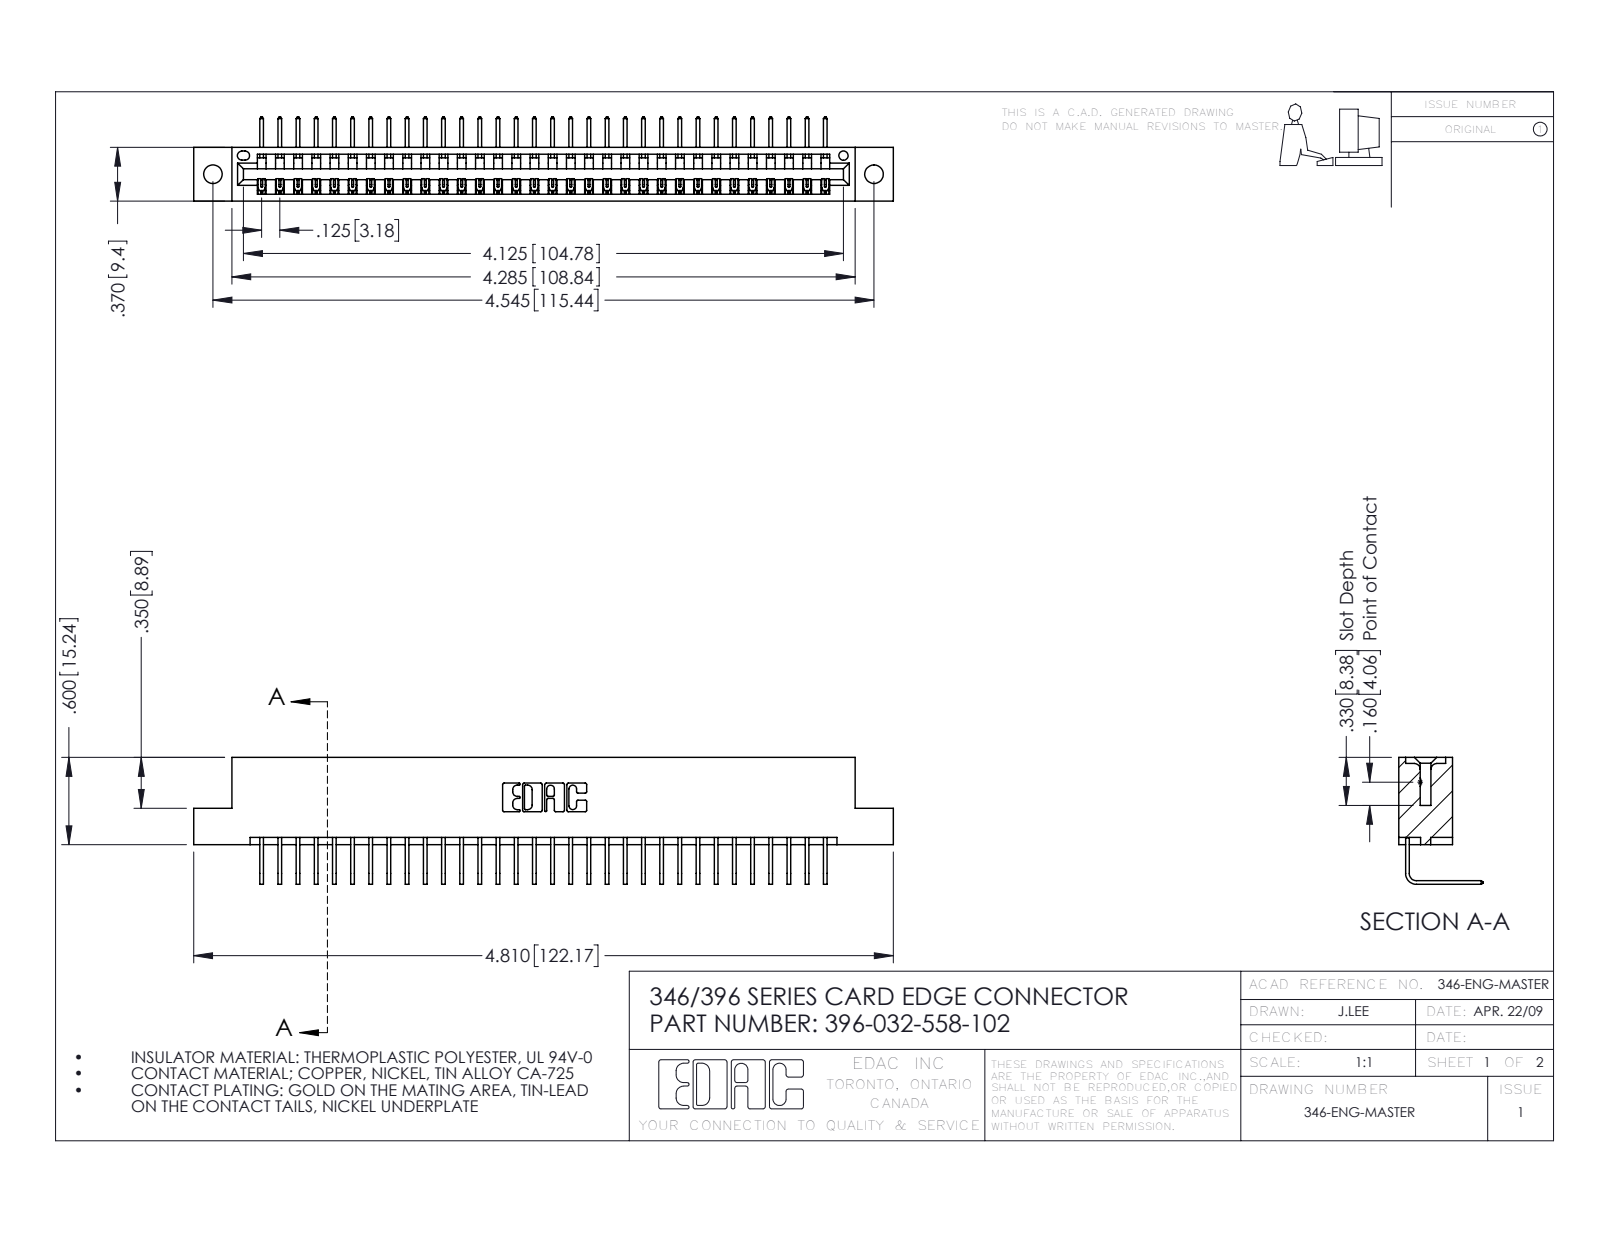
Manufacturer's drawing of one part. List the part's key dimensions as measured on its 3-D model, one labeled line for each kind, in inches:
Part name (STEP PRODUCT): 345-292-001_558 Tail - 2; 396-032-558-102; 346 Part_Flush Mounting Lugs - 0.128 Dia
STEP written by: SolidWorks 2016 (CONFIG_CONTROL_DESIGN)
Units: inches
Bodies: 33 solids, 2042 faces (1420 planar, 622 cylindrical, 0 other)
Overall size (bounding box): 4.81 × 0.873 × 0.58
Volume: 0.714 in³ · Surface area: 23.06 in²
Round holes (diameter × count): ⌀0.128 ×2, ⌀0.064 ×1
Partial cylindrical surfaces — rounded edges, fillets, slot ends (radius × count): R0.006 ×64, R0.01 ×22, R0.007 ×6, R0.031 ×6, R0.026 ×3, R0.031 ×2, R0.04 ×2, R0.014 ×1
Main face-to-face distances: 0.322, 0.048, 0.37, 0.25, 0.298, 0.025, 0.072, 0.148, 0.222, 0.1
Hole centre spacings: 0.246, 4.337, 4.545
